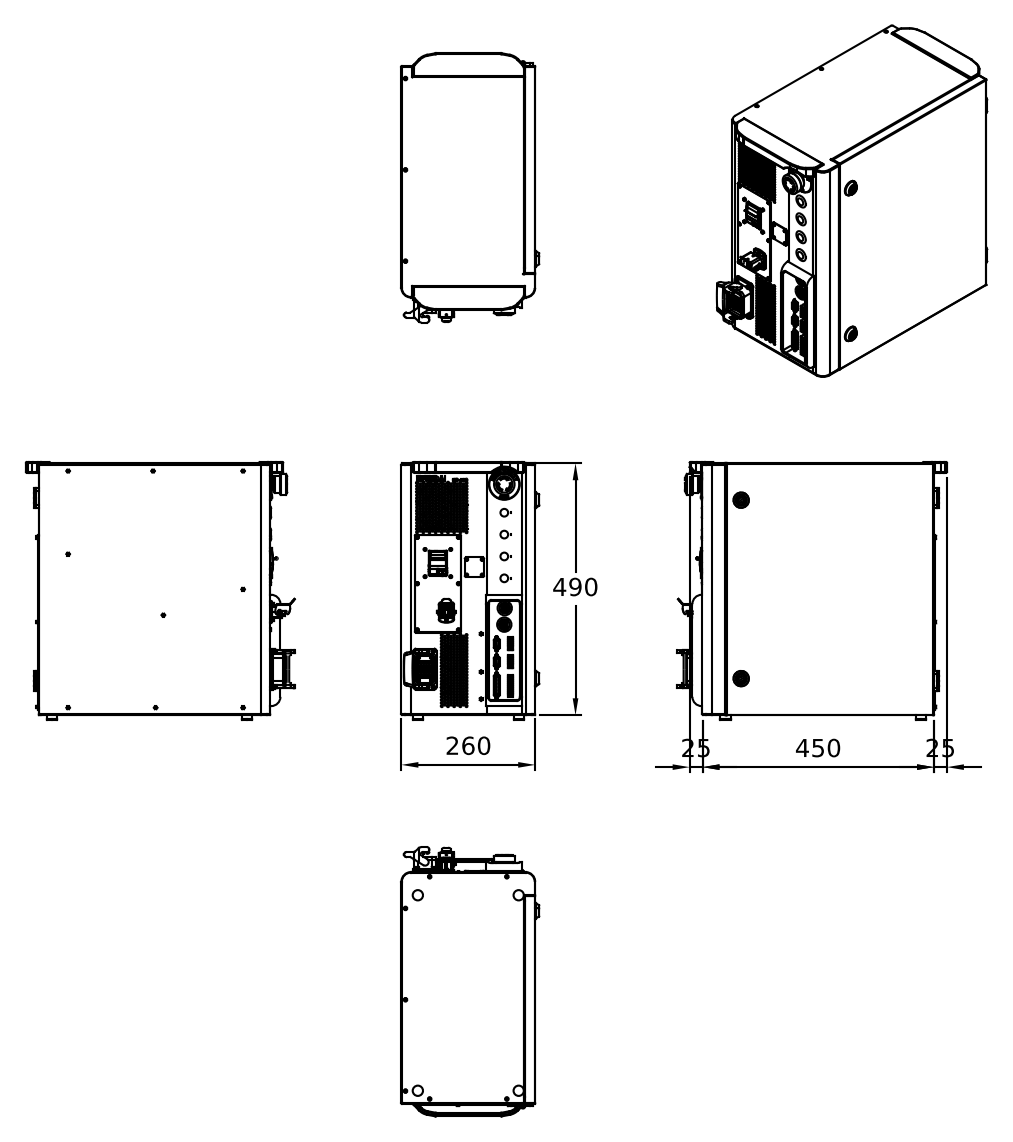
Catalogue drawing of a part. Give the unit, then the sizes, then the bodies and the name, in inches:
Units: inches
Overall size (bounding box): 20.61 × 19.78 × 10.551
Round holes (diameter × count): ⌀0.157 ×508, ⌀0.165 ×48, ⌀0.09 ×43, ⌀0.098 ×41, ⌀0.197 ×41, ⌀0.13 ×35, ⌀0.118 ×28, ⌀0.177 ×26, ⌀0.283 ×18, ⌀0.173 ×17, ⌀0.268 ×16, ⌀0.866 ×10
Round bosses / shafts (diameter × count): ⌀0.024 ×43, ⌀0.118 ×33, ⌀0.197 ×28, ⌀0.217 ×19, ⌀0.28 ×18, ⌀0.165 ×15, ⌀0.157 ×15, ⌀0.236 ×11
Partial cylindrical surfaces — rounded edges, fillets, slot ends (radius × count): R0.02 ×499, R0.008 ×428, R0.012 ×161, R0.039 ×154, R0.079 ×75, R0.157 ×45, R0.197 ×43, R0.01 ×40
Main face-to-face distances: 0.047, 10.189, 19.22, 10.142, 10.236, 17.669, 19.173, 19.268, 17.622, 17.717
Hole centre spacings: 3.937, 6.496, 0.591, 7.596, 1.969, 2.087, 2.559, 2.913
Bodies: 0 solids, 17883 faces (10942 planar, 5137 cylindrical, 1804 other)
STEP written by: SolidWorks 2020 (AUTOMOTIVE_DESIGN)
